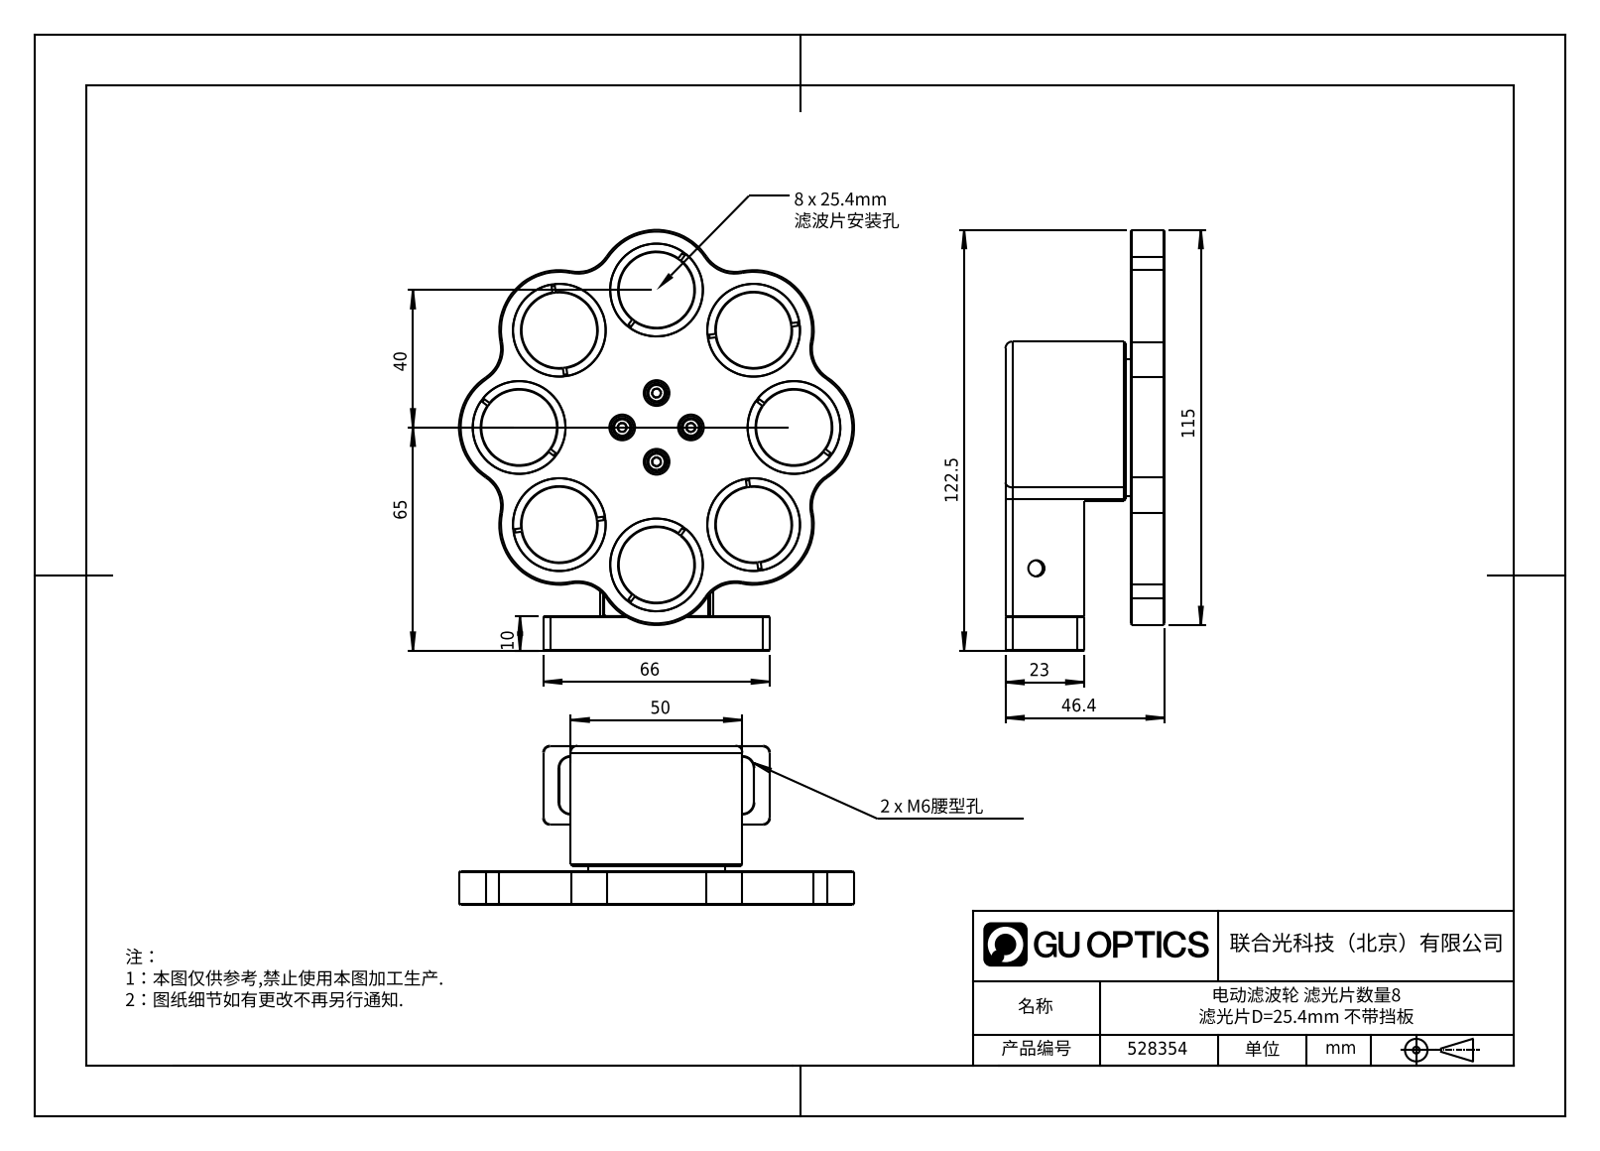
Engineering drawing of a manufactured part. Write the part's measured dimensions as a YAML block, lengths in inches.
part_name: "528354"
step_written_by: "SolidWorks 2020 (CONFIG_CONTROL_DESIGN)"
units: inches
bodies: {solids: 0, faces: 473, planar: 260, cylindrical: 99, other: 114}
overall_size: [4.823, 4.528, 1.827]
round_holes:
  - {diameter: 0.906, count: 8}
  - {diameter: 1.024, count: 8}
  - {diameter: 0.256, count: 4}
  - {diameter: 0.315, count: 4}
  - {diameter: 1.063, count: 4}
  - {diameter: 0.185, count: 1}
round_bosses_or_shafts:
  - {diameter: 0.866, count: 8}
  - {diameter: 0.217, count: 4}
  - {diameter: 0.205, count: 4}
  - {diameter: 0.276, count: 2}
  - {diameter: 0.138, count: 2}
  - {diameter: 1.575, count: 1}
partial_cylinders:
  - {radius: 0.012, count: 20}
  - {radius: 0.394, count: 8}
  - {radius: 0.689, count: 8}
  - {radius: 0.079, count: 6}
  - {radius: 0.13, count: 4}
  - {radius: 0.197, count: 2}
  - {radius: 0.984, count: 1}
face_to_face_distances: [0.394, 0.039, 0.354, 0.236, 0.197, 0.157, 1.433, 1.472, 1.669, 1.827]
hole_center_spacings: [1.623, 1.205, 2.227, 0.557, 1.181, 1.326, 1.326, 1.874]
